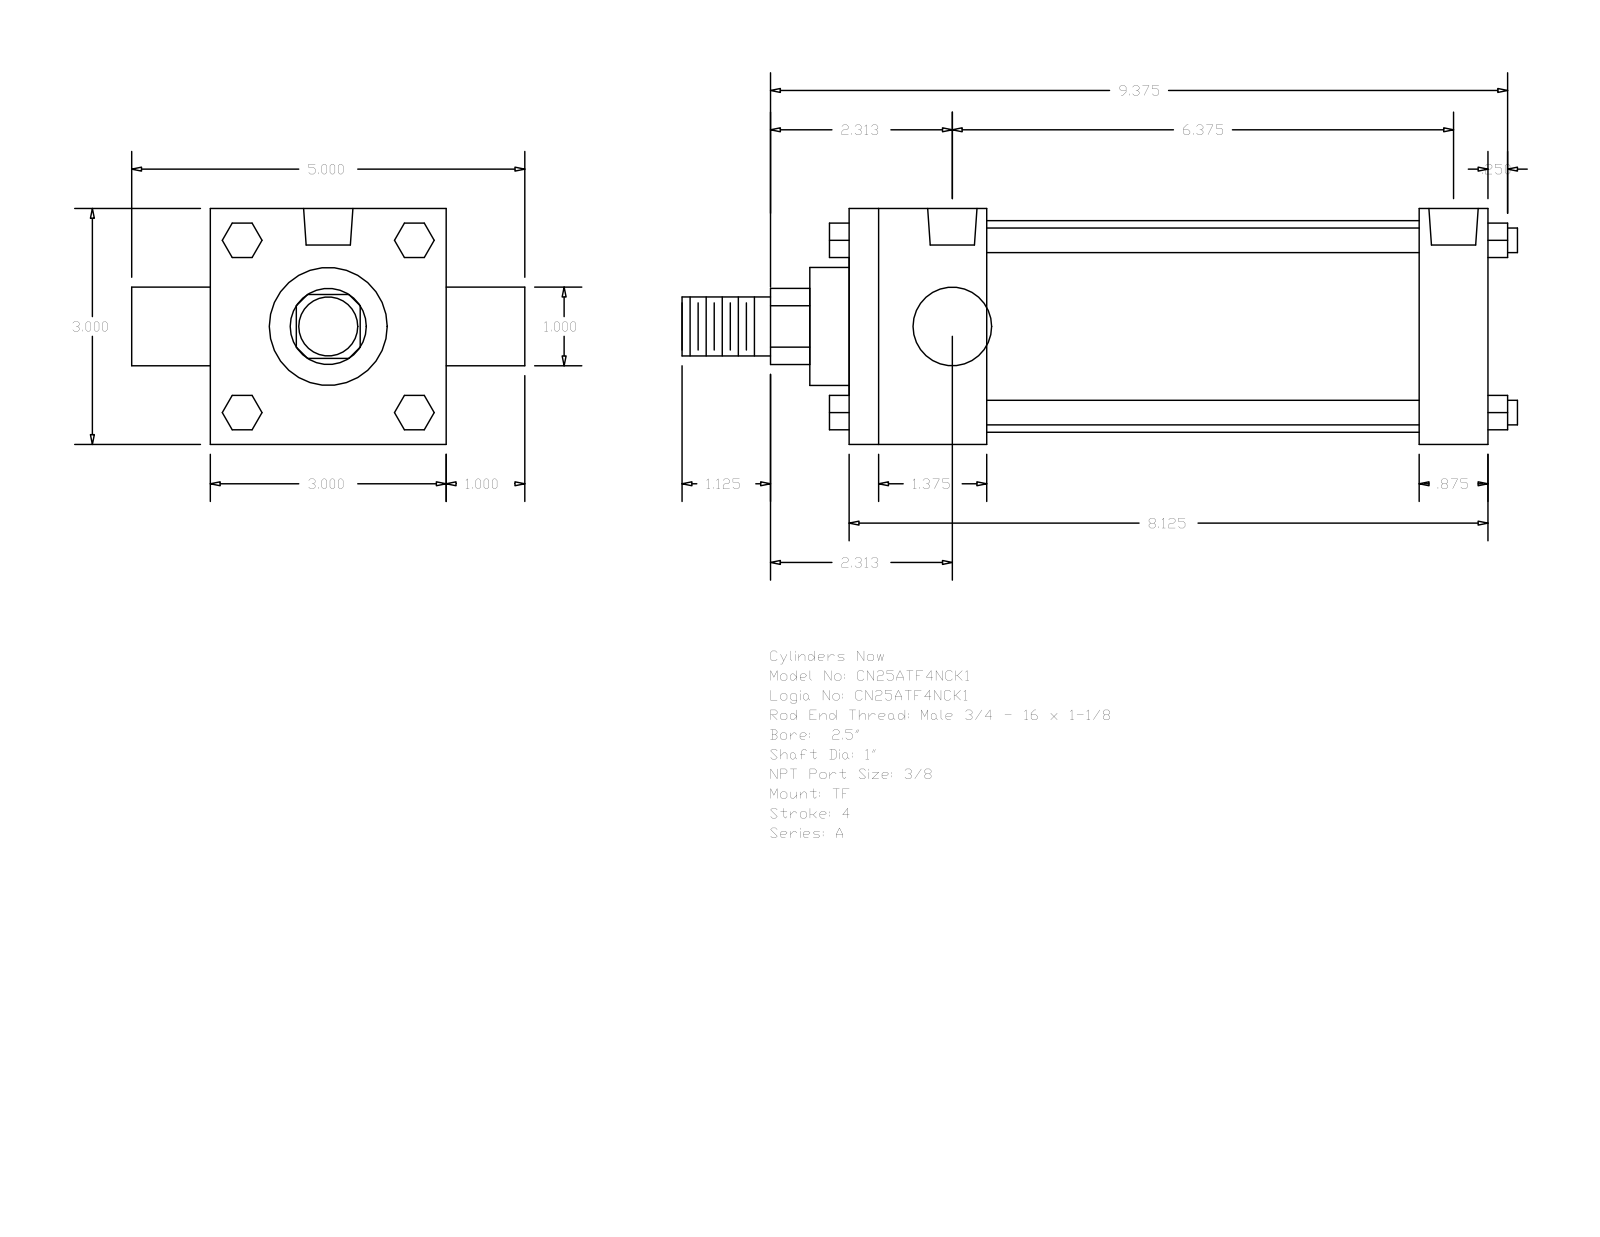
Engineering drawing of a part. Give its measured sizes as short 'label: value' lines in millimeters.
name: A_TF__0250_1
written by: GSSL Pune (CONFIG_CONTROL_DESIGN)
unit: mm
bodies: 0 solids, 120 faces (92 planar, 28 cylindrical, 0 other)
size: 269.88 × 127 × 76.2
holes: 3× ⌀5.56, 2× ⌀15.93
bosses: 4× ⌀7.94, 2× ⌀25.4, 1× ⌀68.33, 1× ⌀38.1, 1× ⌀19.05
rounds: 1× R12.29
face distances: 76.2, 206.38, 44.45, 184.15, 139.7, 161.93, 22.23, 25.4, 101.6, 12.7
hole spacings: 2.38, 164.3, 161.92, 166.68
